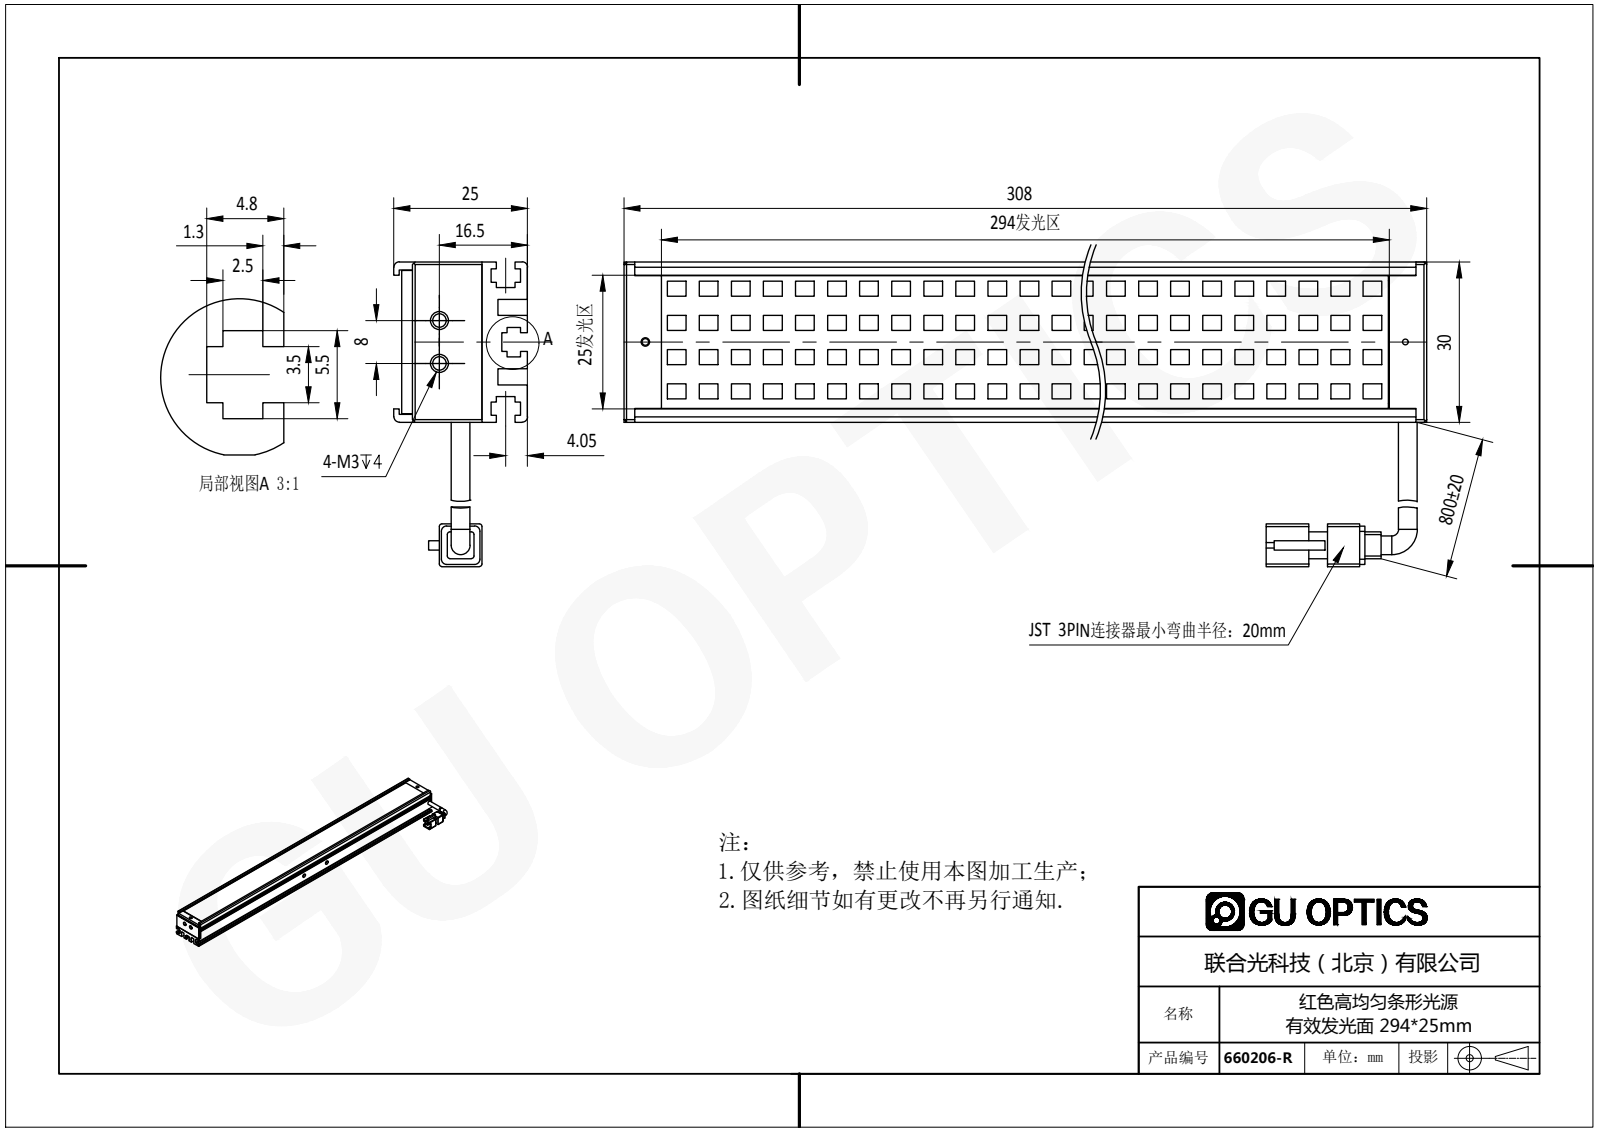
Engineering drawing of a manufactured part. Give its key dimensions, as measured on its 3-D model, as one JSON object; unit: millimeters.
{"part_name": "660206-R", "step_written_by": "SolidWorks 2016 (AUTOMOTIVE_DESIGN)", "units": "millimeters", "bodies": {"solids": 6, "faces": 1424, "planar": 1238, "cylindrical": 83, "other": 103}, "overall_size": [308, 57, 25], "volume_mm3": 104401, "surface_area_mm2": 106510, "round_holes": [[1.6, 5], [1.5, 2], [1.7, 2], [2.5, 2], [2.8, 2], [3, 2], [1.1, 1], [1.25, 1], [2, 1]], "round_bosses_or_shafts": [[3.5, 2]], "partial_cylinders_radius": [[1, 12], [0.5, 8], [1.65, 1]], "face_to_face_distances": [1, 13, 2, 2.5, 3, 27.5, 9.5, 4.5, 12, 15.1], "hole_center_spacings": [300, 7, 135, 135.16, 165, 165.13, 300.08, 8]}
